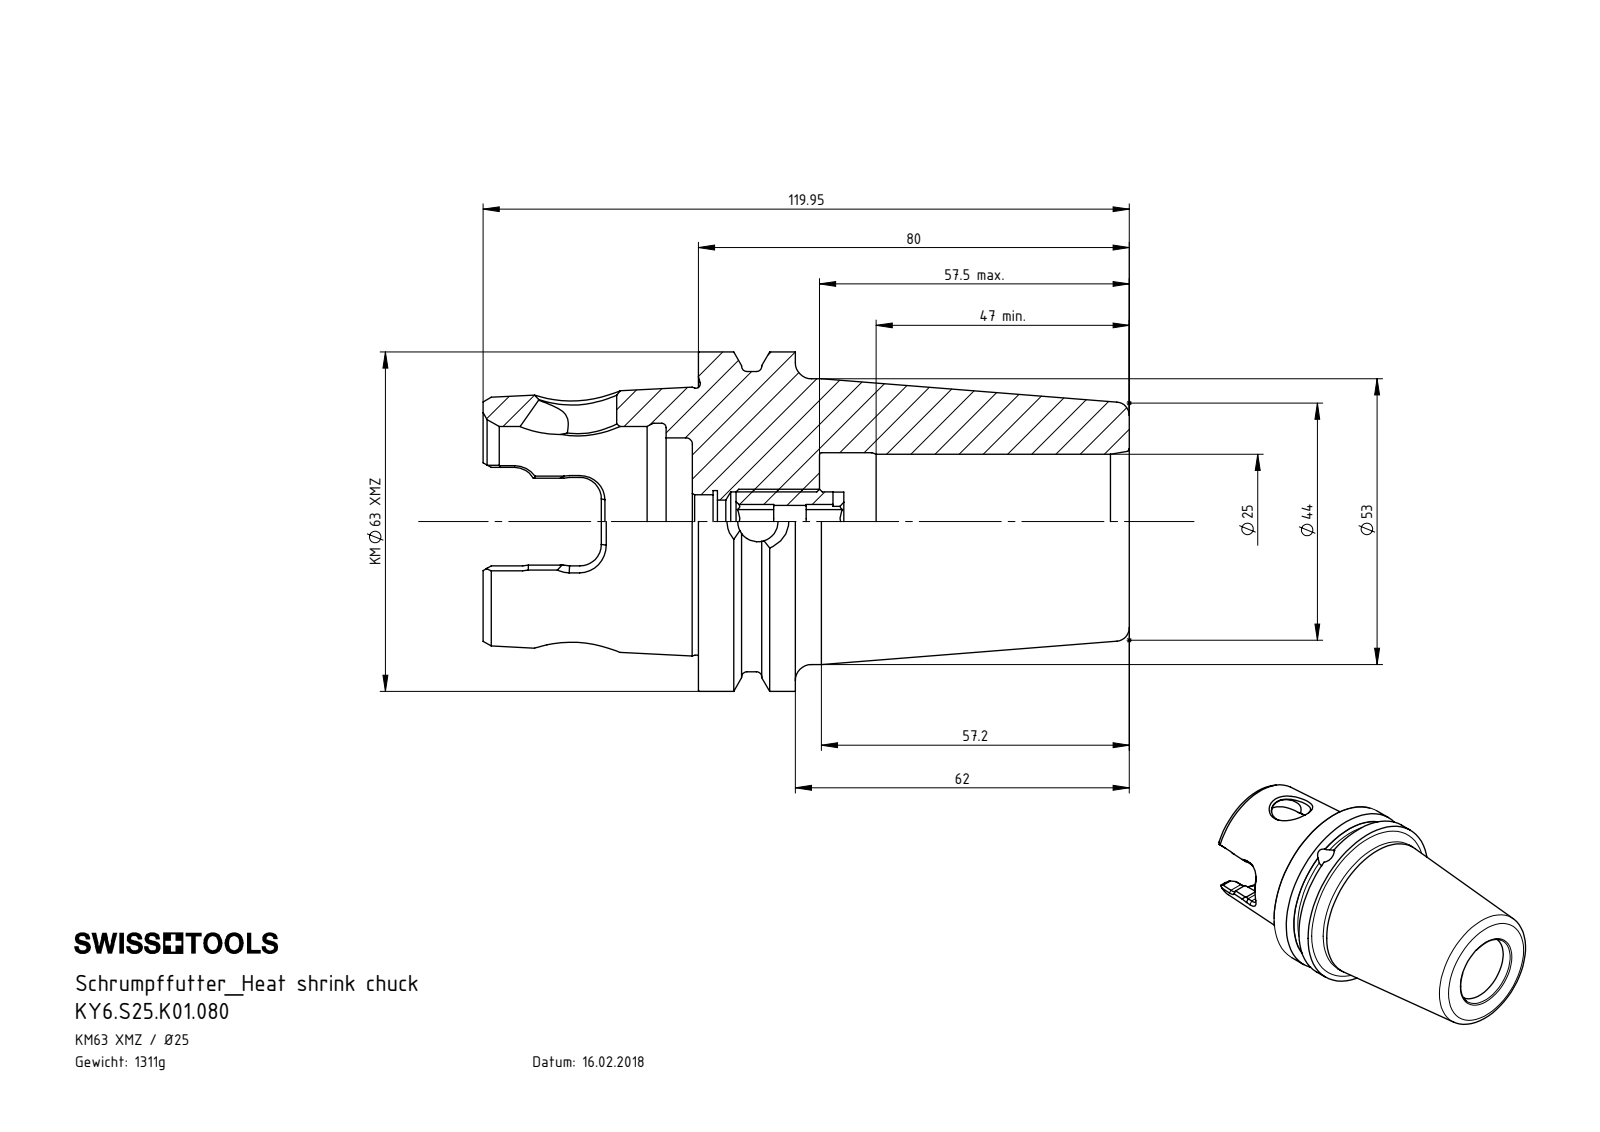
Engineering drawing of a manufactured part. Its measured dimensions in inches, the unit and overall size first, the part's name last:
Units: inches
Overall size (bounding box): 4.722 × 2.478 × 2.478
Round holes (diameter × count): ⌀0.294 ×2, ⌀0.236 ×1, ⌀0.315 ×1, ⌀0.334 ×1, ⌀0.394 ×1, ⌀0.433 ×1, ⌀0.453 ×1, ⌀0.571 ×1, ⌀0.984 ×1, ⌀1.008 ×1, ⌀1.224 ×1, ⌀1.389 ×1
Round bosses / shafts (diameter × count): ⌀2.478 ×1, ⌀2.193 ×1, ⌀2.087 ×1, ⌀0.472 ×1
Partial cylindrical surfaces — rounded edges, fillets, slot ends (radius × count): R0.157 ×6, R0.277 ×2
Main face-to-face distances: 3.15, 0.043, 3.193, 0.709, 0.177, 0.752, 2.441, 0.929, 0.886, 2.264
Volume: 10.19 in³ · Surface area: 53.78 in²
Bodies: 2 solids, 277 faces (79 planar, 60 cylindrical, 138 other)
Part name (STEP PRODUCT): ERU-AN5.K01.020_A; KY6-S25.K01.080_A; KY6.S25.K01.080
STEP written by: SolidWorks 2017 (CONFIG_CONTROL_DESIGN)
